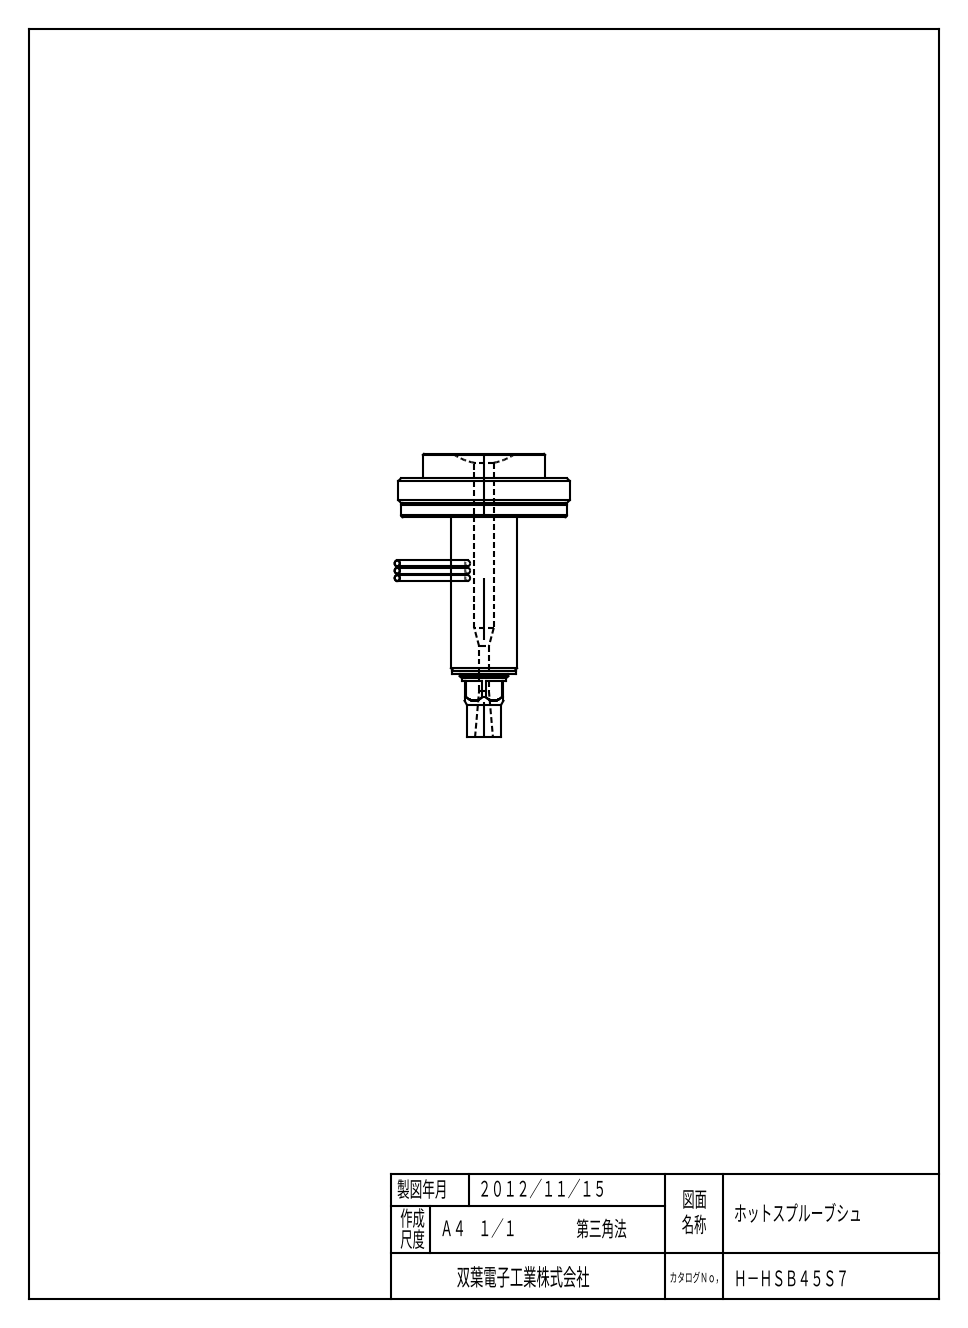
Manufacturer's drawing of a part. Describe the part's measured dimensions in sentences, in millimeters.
The part is named "HSB45S7". Its 3-D file was written by "SIEMENS PLM Software NX 2023 (AUTOMOTIVE_DESIGN)". It is 1 solid with 79 faces: 23 planar, 30 cylindrical and 26 other. Overall it measures 160.34 by 160.34 by 58 millimeters. Its volume is 13 974 cubic millimeters and its surface area 8 057 square millimeters. Round holes: 4 of diameter 5.5, 4 of diameter 8.9, 1 of diameter 4, 1 of diameter 16. Round bosses or shafts: 3 of diameter 4, 3 of diameter 1.2, 1 of diameter 35, 1 of diameter 34, 1 of diameter 13.5, 1 of diameter 13, 1 of diameter 10, 1 of diameter 9.98. Partial cylindrical surfaces (rounded edges, fillets, slot ends): 1 of radius 12.5. The main face-to-face distances are 5, 8, 13, 0.5, 7.5, 5.5, 3, 2.5, 32.06, 37.06. The hole center spacings are 12.5, 17.68, 25.
